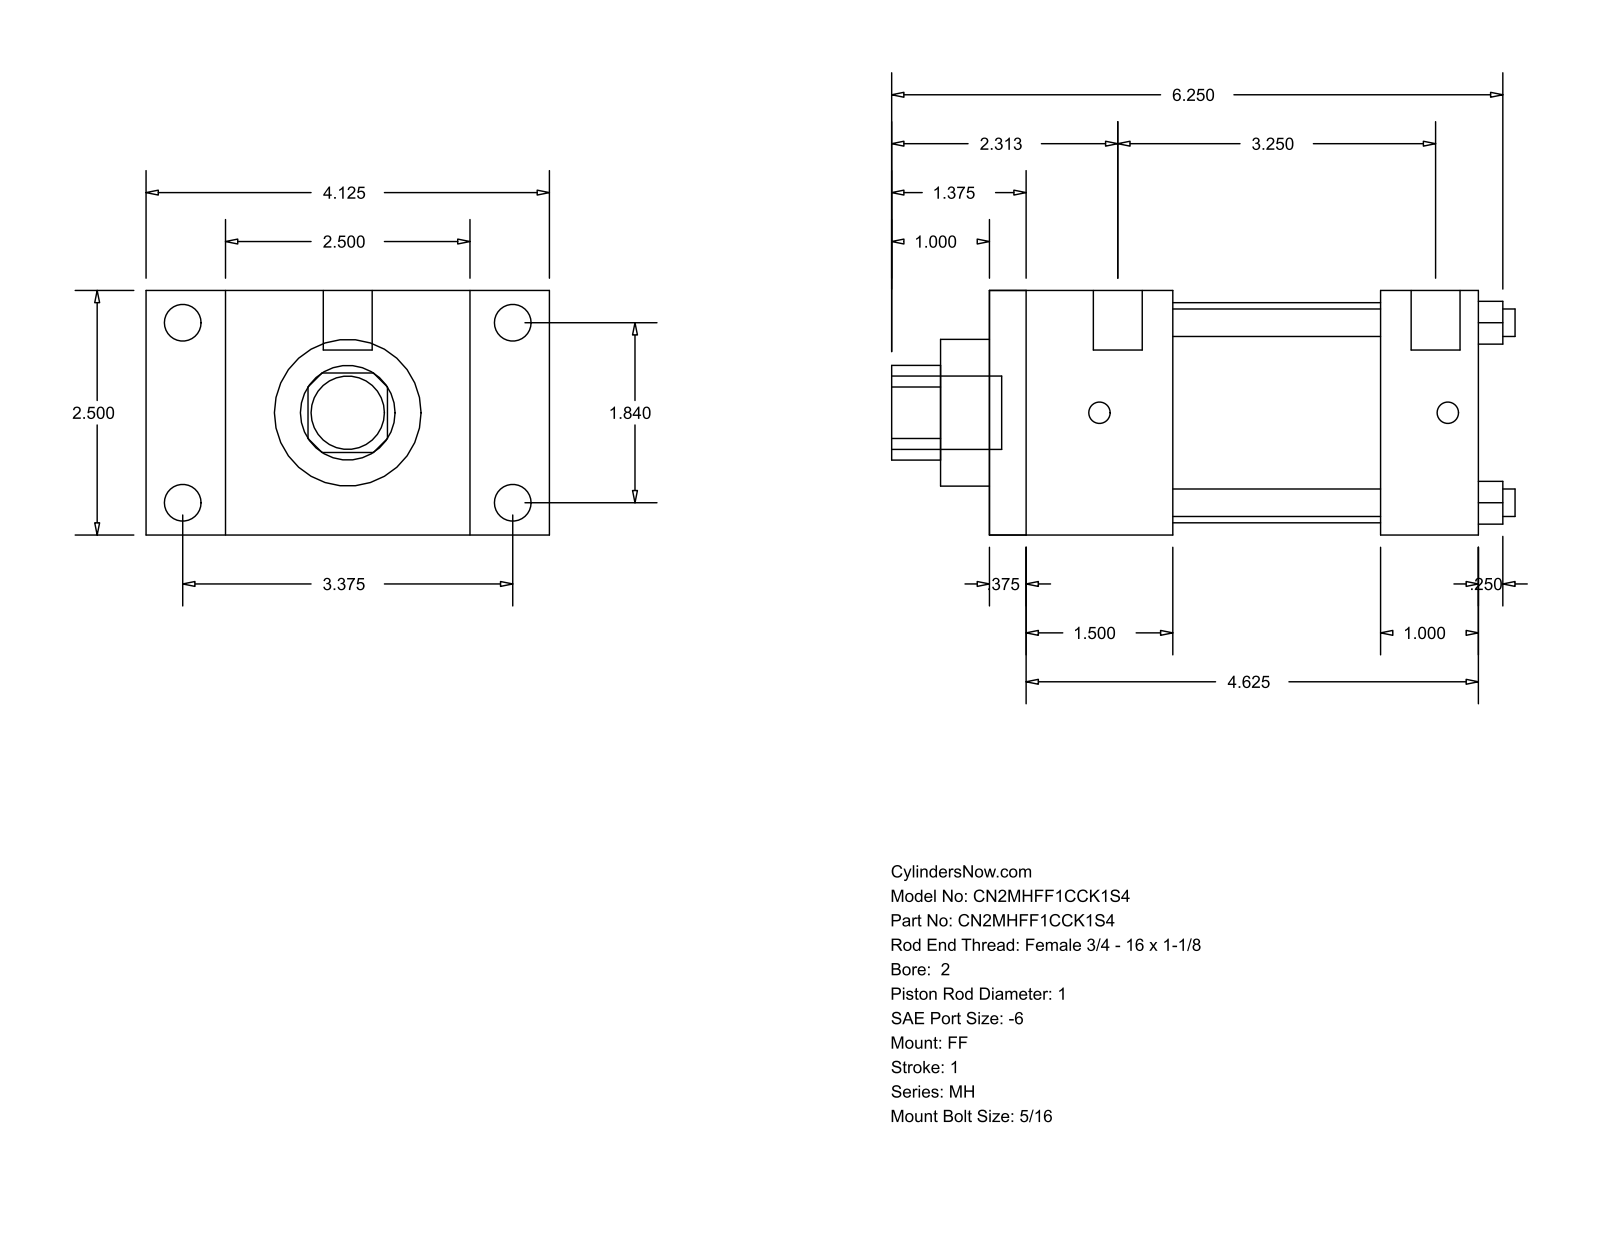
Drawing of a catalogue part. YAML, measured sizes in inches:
part_name: "MH_FF__0200_1"
step_written_by: "GSSL Pune (CONFIG_CONTROL_DESIGN)"
units: inches
bodies: {solids: 0, faces: 92, planar: 64, cylindrical: 28, other: 0}
overall_size: [6.375, 4.125, 2.5]
round_holes:
  - {diameter: 0.281, count: 4}
  - {diameter: 1, count: 1}
  - {diameter: 1.5, count: 1}
  - {diameter: 2.25, count: 1}
round_bosses_or_shafts:
  - {diameter: 0.375, count: 4}
  - {diameter: 0.219, count: 4}
  - {diameter: 0.5, count: 2}
  - {diameter: 0.75, count: 1}
partial_cylinders:
  - {radius: 0.484, count: 1}
face_to_face_distances: [2.5, 5, 0.375, 4.625, 0.813, 1, 1.875, 4, 1.5, 3.625]
hole_center_spacings: [1.301, 1.84, 2.602]
